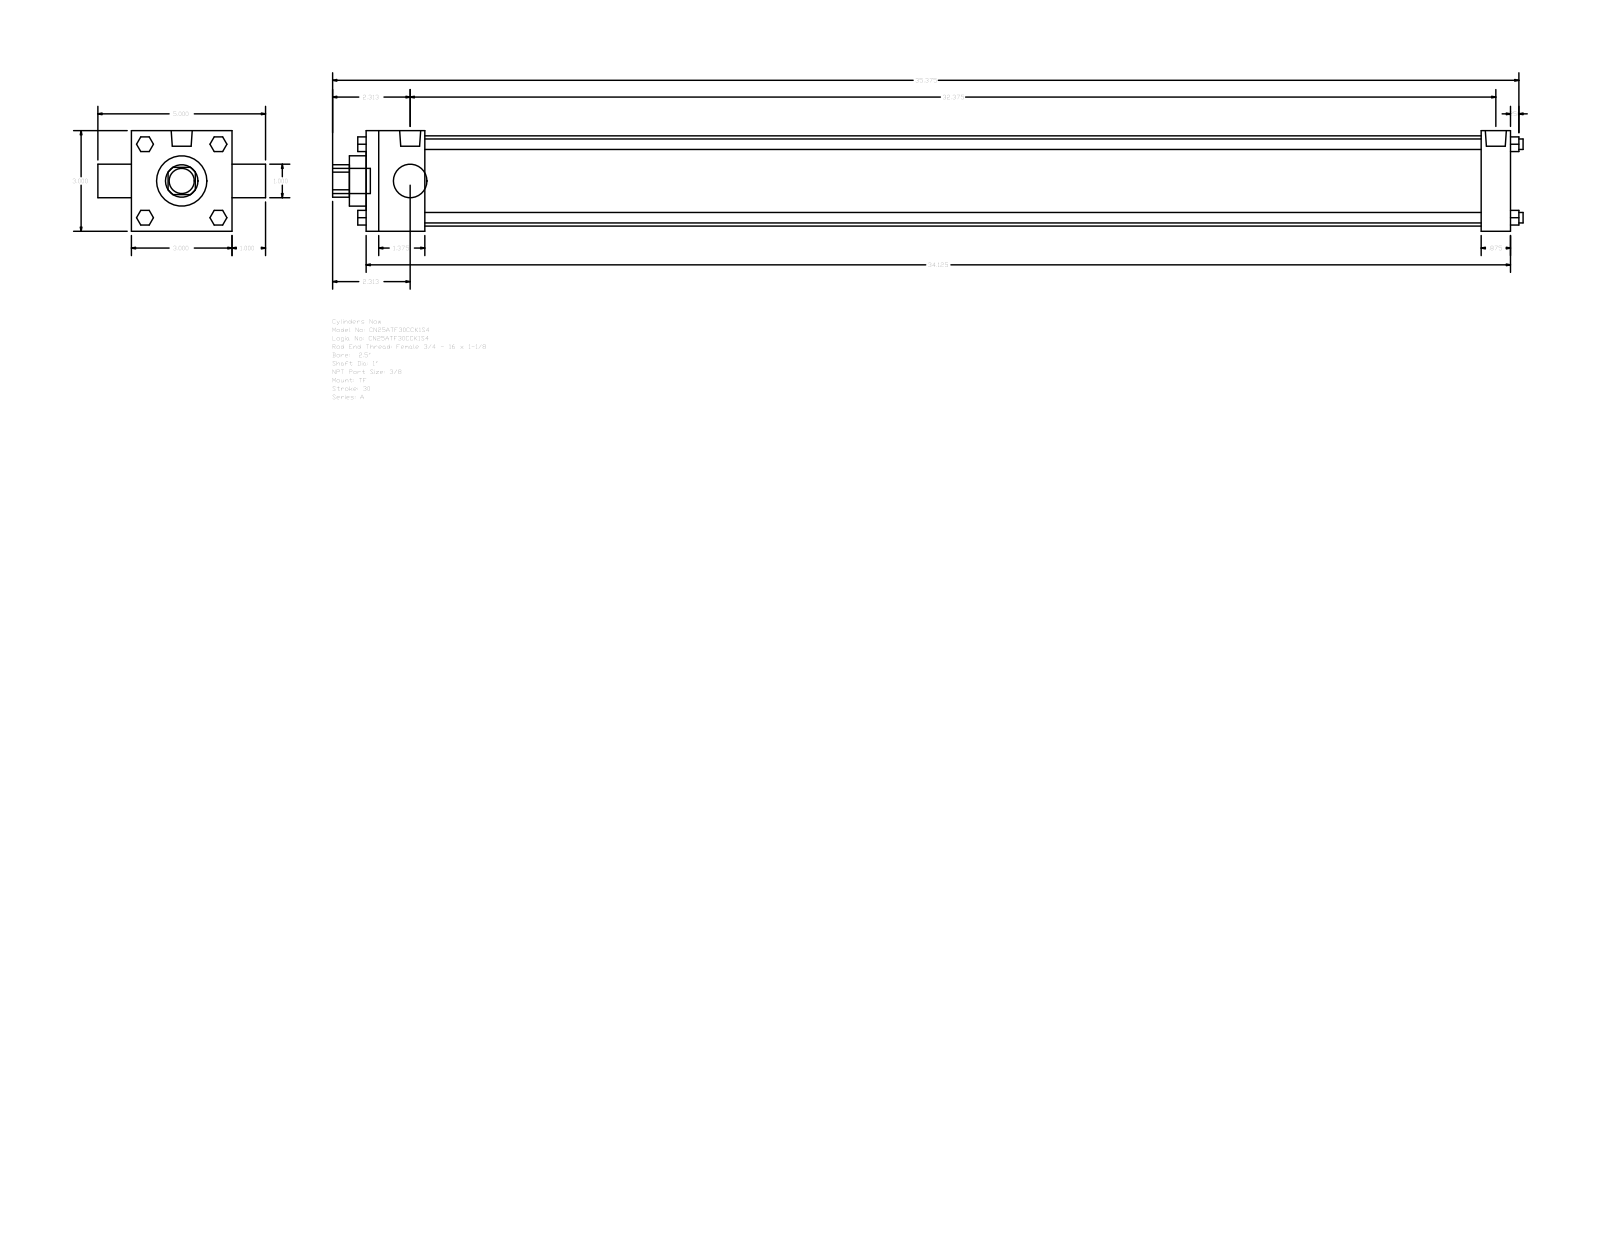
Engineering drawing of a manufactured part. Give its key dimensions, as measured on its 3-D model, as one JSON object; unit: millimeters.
{"part_name": "A_TF__0250_1", "step_written_by": "GSSL Pune (CONFIG_CONTROL_DESIGN)", "units": "millimeters", "bodies": {"solids": 0, "faces": 120, "planar": 92, "cylindrical": 28, "other": 0}, "overall_size": [901.7, 127, 76.2], "round_holes": [[25.4, 2], [38.1, 1], [68.33, 1]], "round_bosses_or_shafts": [[7.94, 4], [5.56, 3], [15.93, 2], [19.05, 1]], "partial_cylinders_radius": [[12.29, 1]], "face_to_face_distances": [76.2, 866.77, 44.45, 844.55, 800.1, 822.32, 22.22, 25.4, 101.6, 879.47]}
